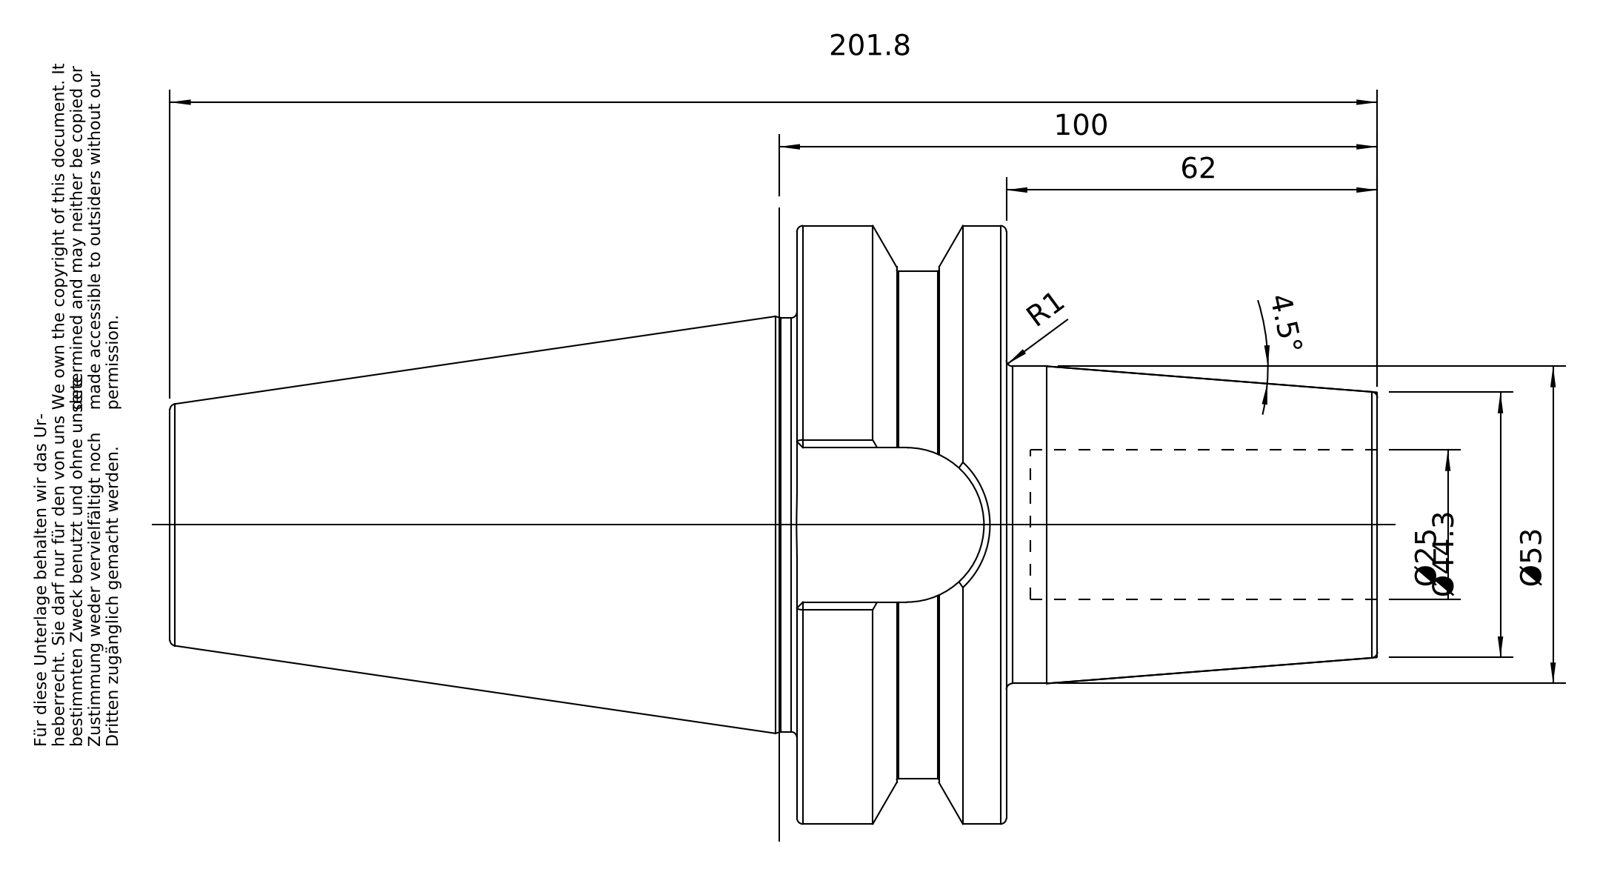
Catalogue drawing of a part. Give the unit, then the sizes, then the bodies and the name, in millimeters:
Units: millimetres
Overall size (bounding box): 201.8 × 99.97 × 99.97
Round holes (diameter × count): ⌀20.75 ×1, ⌀25 ×1, ⌀25.02 ×1, ⌀25.7 ×1
Round bosses / shafts (diameter × count): ⌀99.97 ×1, ⌀84.75 ×1, ⌀69.15 ×1, ⌀53 ×1, ⌀24.01 ×1
Partial cylindrical surfaces — rounded edges, fillets, slot ends (radius × count): R12.9 ×1
Main face-to-face distances: 35, 97, 62, 70.4, 104.8, 139.8, 201.8, 143.8, 39, 4
Volume: 557 449 mm³ · Surface area: 65 211 mm²
Bodies: 1 solid, 96 faces (26 planar, 22 cylindrical, 48 other)
Part name (STEP PRODUCT): 50-640-25
STEP written by: PRO/ENGINEER BY PARAMETRIC TECHNOLOGY CORPORATION, 2010430 (CONFIG_CONTROL_DESIGN)
